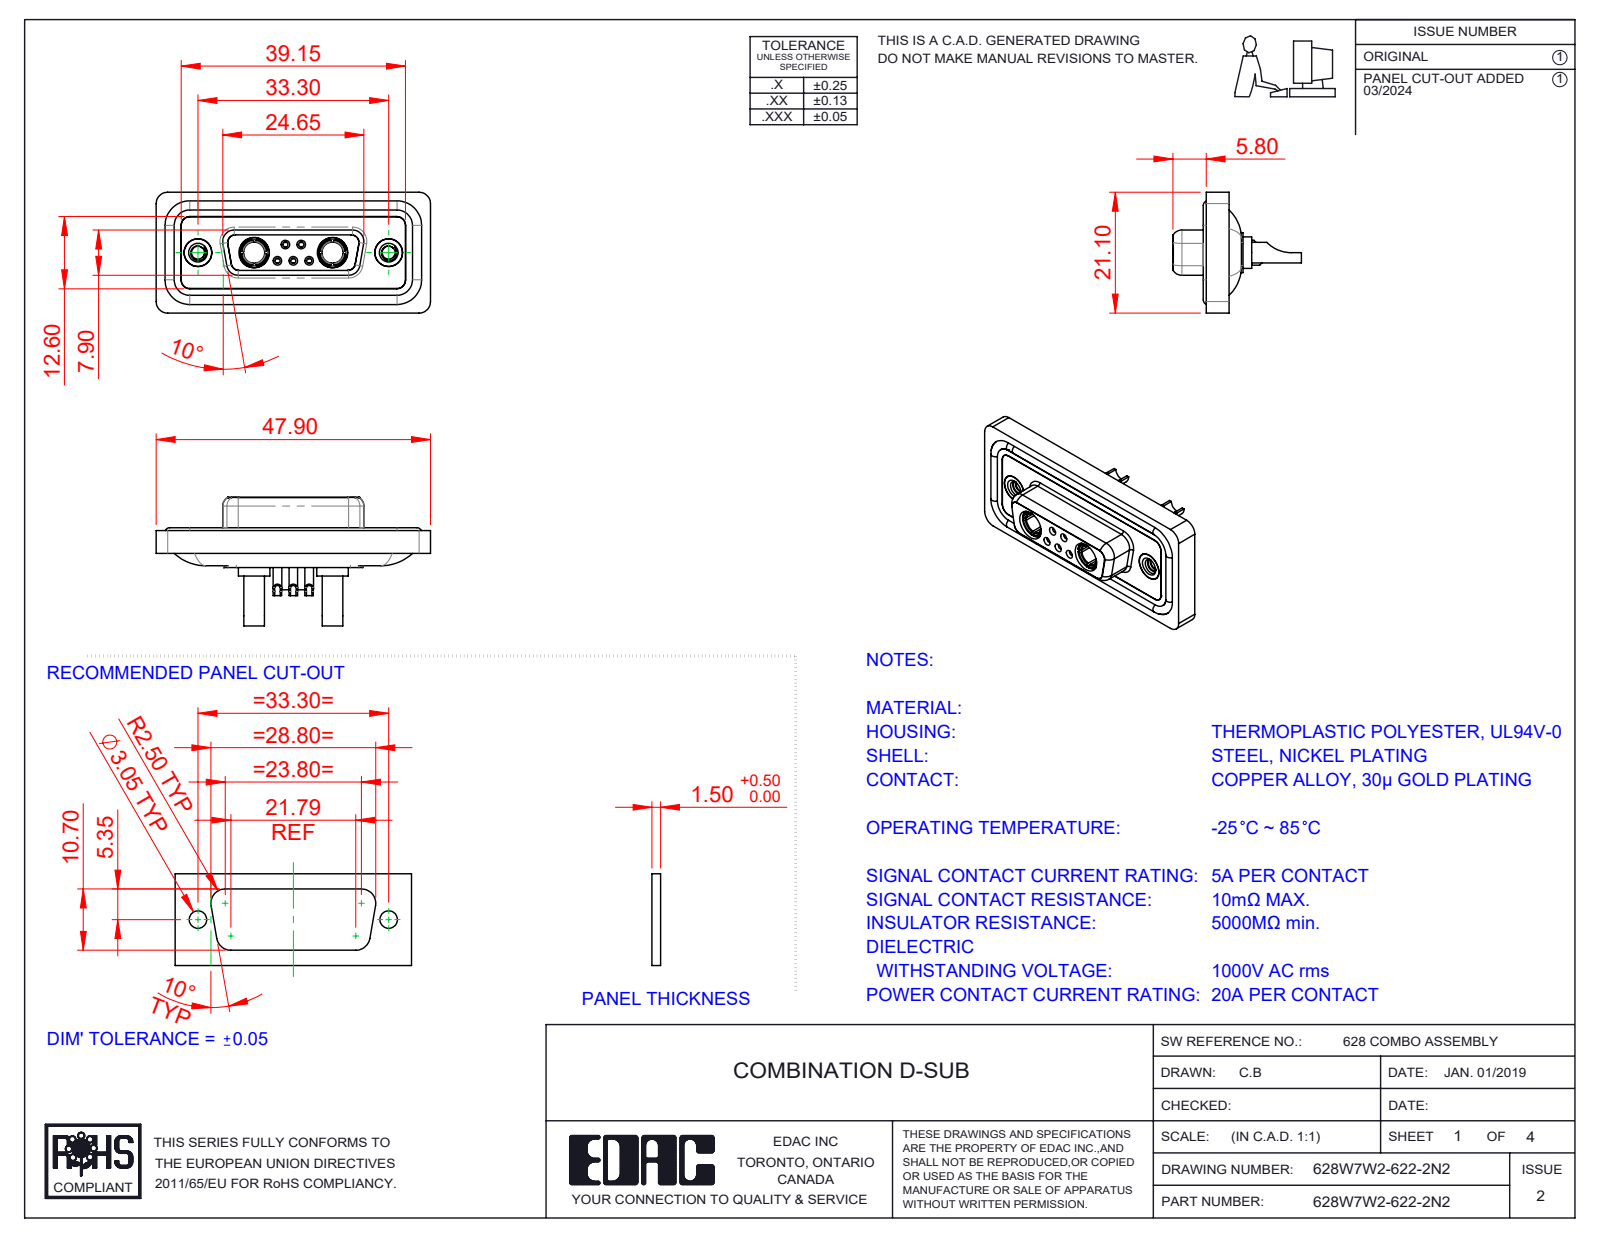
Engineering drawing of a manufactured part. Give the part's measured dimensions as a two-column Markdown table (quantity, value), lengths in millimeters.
| quantity | value |
| --- | --- |
| part name | 628Combo Contact Row 1_22; 628Combo Housing_7W2; 628Combo Shell Rear_15 Contacts; 628Combo Shell Front_15 Contacts (+5 more) |
| STEP written by | SolidWorks 2023 (CONFIG_CONTROL_DESIGN) |
| units | millimeters |
| bodies | 16 solids, 821 faces (254 planar, 345 cylindrical, 222 other) |
| overall size | 47.9 × 22.45 × 21.1 |
| volume | 6 114 mm³ |
| surface area | 10 105 mm² |
| round holes (diameter × count) | 0.9 × 5, 1 × 5, 1.1 × 5, 1.5 × 5, 2 × 5, 4.85 × 4, 1.6 × 3, 1.7 × 2, 2.26 × 2, 2.7 × 2, 3.7 × 2, 4 × 2 |
| round bosses / shafts (diameter × count) | 1.6 × 6, 2.2 × 5, 5.5 × 2, 5.2 × 2, 4.96 × 2, 4.95 × 2, 4.8 × 2, 4.75 × 2 |
| partial cylindrical surfaces (radius × count) | 1.5 × 22, 2 × 20, 1.35 × 12, 1.6 × 8, 1 × 6, 0.25 × 4, 0.5 × 4, 0.6 × 4 |
| main face-to-face distances | 0.4, 1.8, 1.6, 0.5, 2.9, 1.1, 7.45, 5.65, 6.6, 7.05 |
| hole center spacings | 3.16, 2.77, 9.8, 23.5, 4.31, 4.33, 5.03, 5.04 |
